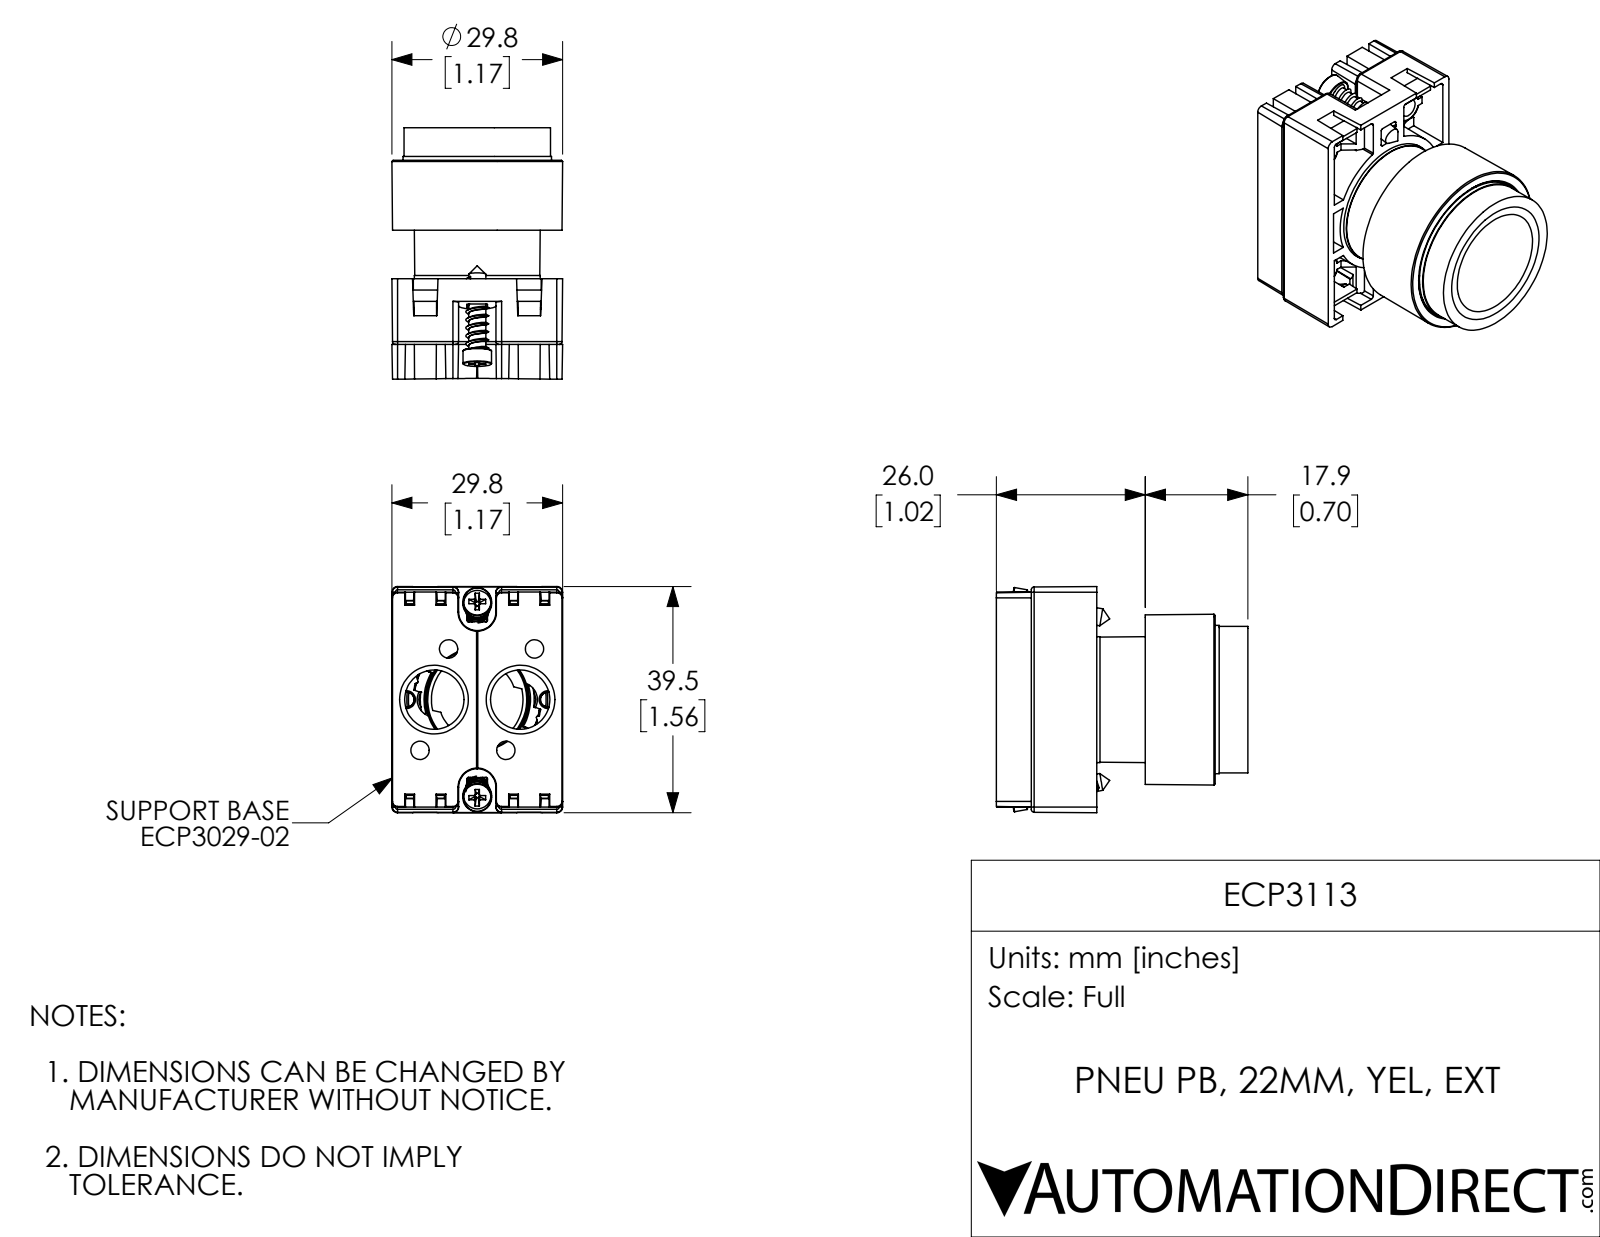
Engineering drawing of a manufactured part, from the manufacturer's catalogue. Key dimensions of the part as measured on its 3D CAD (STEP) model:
Part name (STEP PRODUCT): ECP3113
STEP written by: SolidWorks 2017 (AUTOMOTIVE_DESIGN)
Units: inches
Bodies: 7 solids, 781 faces (364 planar, 133 cylindrical, 284 other)
Overall size (bounding box): 1.728 × 1.555 × 1.173
Volume: 1.025 in³ · Surface area: 29.57 in²
Round holes (diameter × count): ⌀0.081 ×4, ⌀0.407 ×2, ⌀0.697 ×1, ⌀0.732 ×1
Round bosses / shafts (diameter × count): ⌀0.197 ×2, ⌀0.118 ×2, ⌀1.02 ×1, ⌀1.008 ×1, ⌀0.866 ×1
Partial cylindrical surfaces — rounded edges, fillets, slot ends (radius × count): R0.02 ×18, R0.006 ×8, R0.012 ×8, R0.008 ×4, R0.039 ×4, R0.008 ×2, R0.118 ×2, R0.128 ×2
Main face-to-face distances: 1.261, 0.177, 0.067, 0.715, 0.962, 0.811, 0.451, 0.587, 0.528, 0.519
Hole centre spacings: 0.304, 0.541, 0.817, 0.295, 0.472, 0.972, 1.081, 0.591
